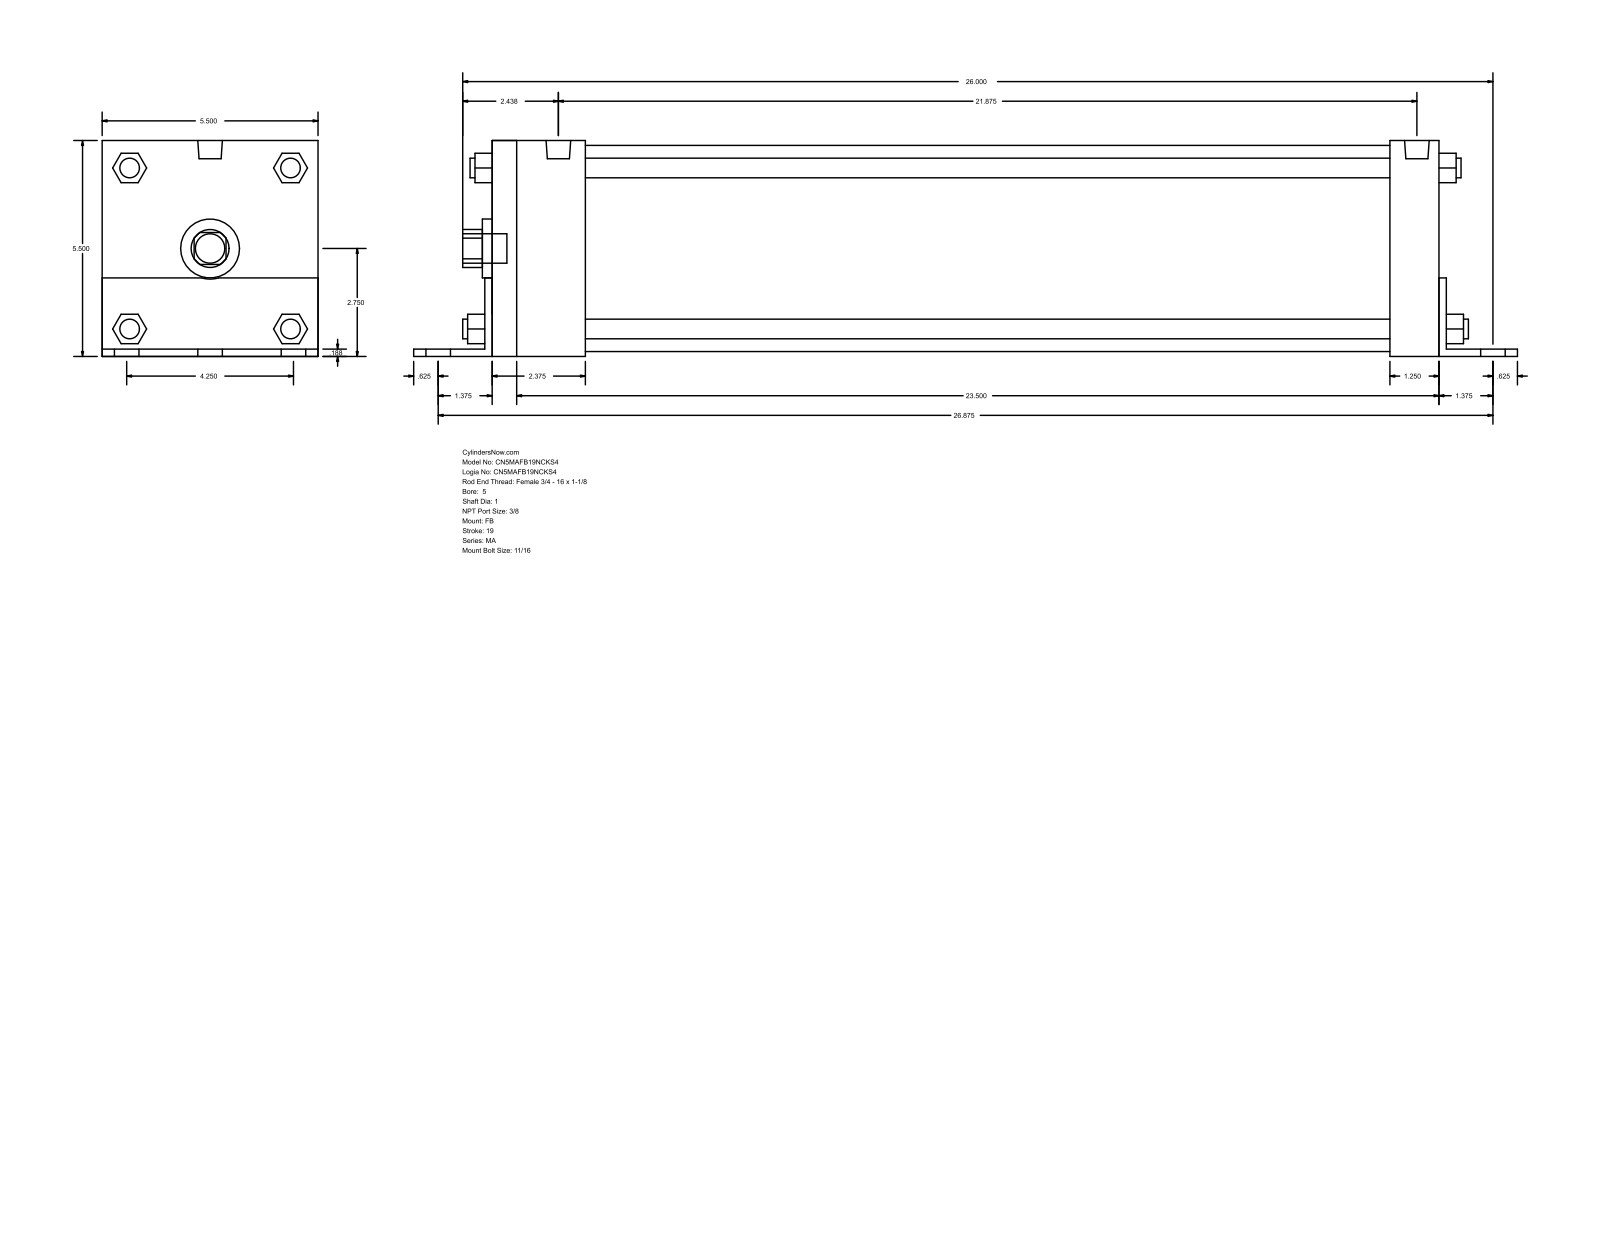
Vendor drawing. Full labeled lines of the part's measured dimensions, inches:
Part name (STEP PRODUCT): MA_FB__0500_1
STEP written by: GSSL Pune (CONFIG_CONTROL_DESIGN)
Units: inches
Bodies: 0 solids, 140 faces (105 planar, 35 cylindrical, 0 other)
Overall size (bounding box): 28.125 × 5.502 × 5.5
Round holes (diameter × count): ⌀1 ×1, ⌀1.5 ×1, ⌀5.25 ×1
Round bosses / shafts (diameter × count): ⌀0.687 ×6, ⌀0.5 ×4, ⌀0.437 ×4, ⌀0.627 ×2, ⌀0.75 ×1
Partial cylindrical surfaces — rounded edges, fillets, slot ends (radius × count): R0.484 ×1, R0.78 ×1
Main face-to-face distances: 5.5, 0.187, 5.502, 24.313, 0.185, 5.315, 24.125, 24.5, 1.437, 1.25
